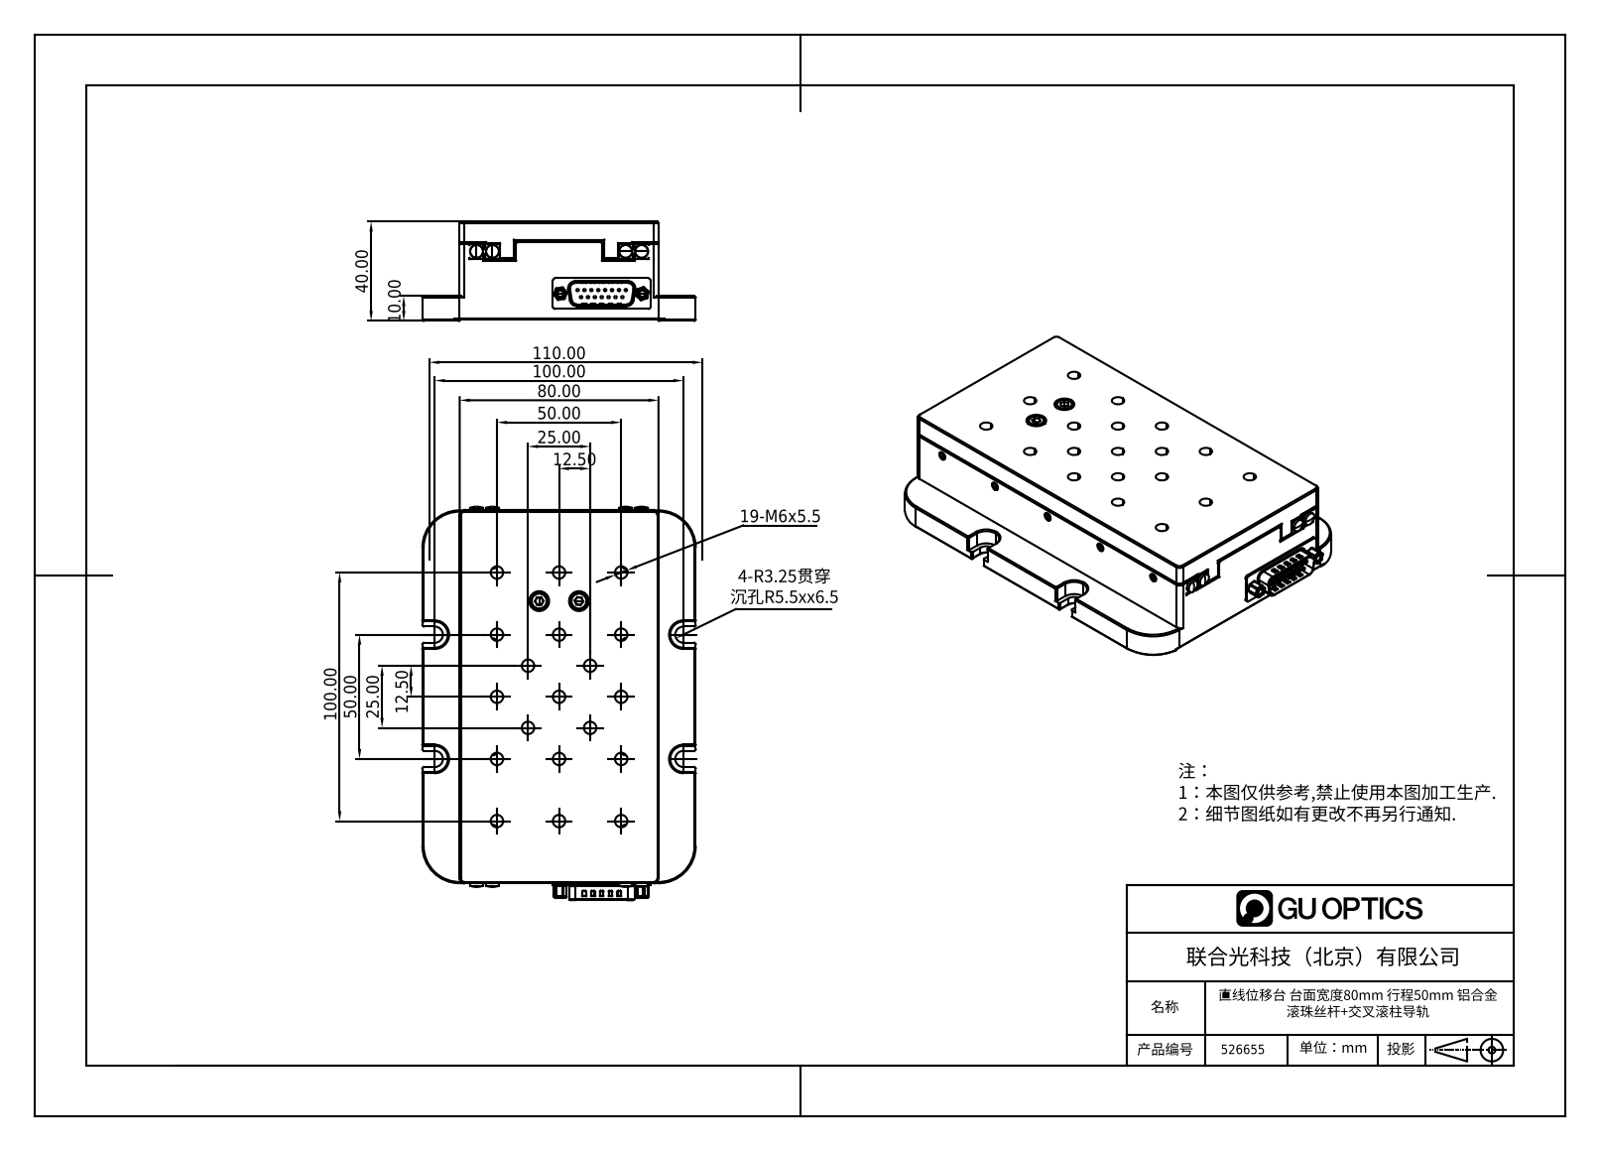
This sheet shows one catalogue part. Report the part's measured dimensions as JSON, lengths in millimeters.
{"part_name": "FMS80R-30", "step_written_by": "SolidWorks 2017 (CONFIG_CONTROL_DESIGN)", "units": "millimeters", "bodies": {"solids": 2, "faces": 2095, "planar": 1026, "cylindrical": 592, "other": 477}, "overall_size": [158.3, 110, 40], "volume_mm3": 514247, "surface_area_mm2": 86582, "round_holes": [[1.5, 22], [6, 20], [5, 19], [2.5, 10], [3.3, 5], [2, 2], [4.5, 2], [8, 2], [3.2, 1]], "round_bosses_or_shafts": [[5.5, 20], [2, 20], [1, 15], [7, 2], [4, 2], [3, 1]], "partial_cylinders_radius": [[0.5, 36], [1, 14], [0.45, 10], [0.4, 8], [2, 8], [0.3, 4], [2.5, 4], [3.25, 4]], "face_to_face_distances": [9, 30.5, 39.5, 0.5, 31, 7.5, 32, 1.5, 15, 1], "hole_center_spacings": [30, 15, 68.66, 73.41, 60, 45, 80.71, 89.94]}
